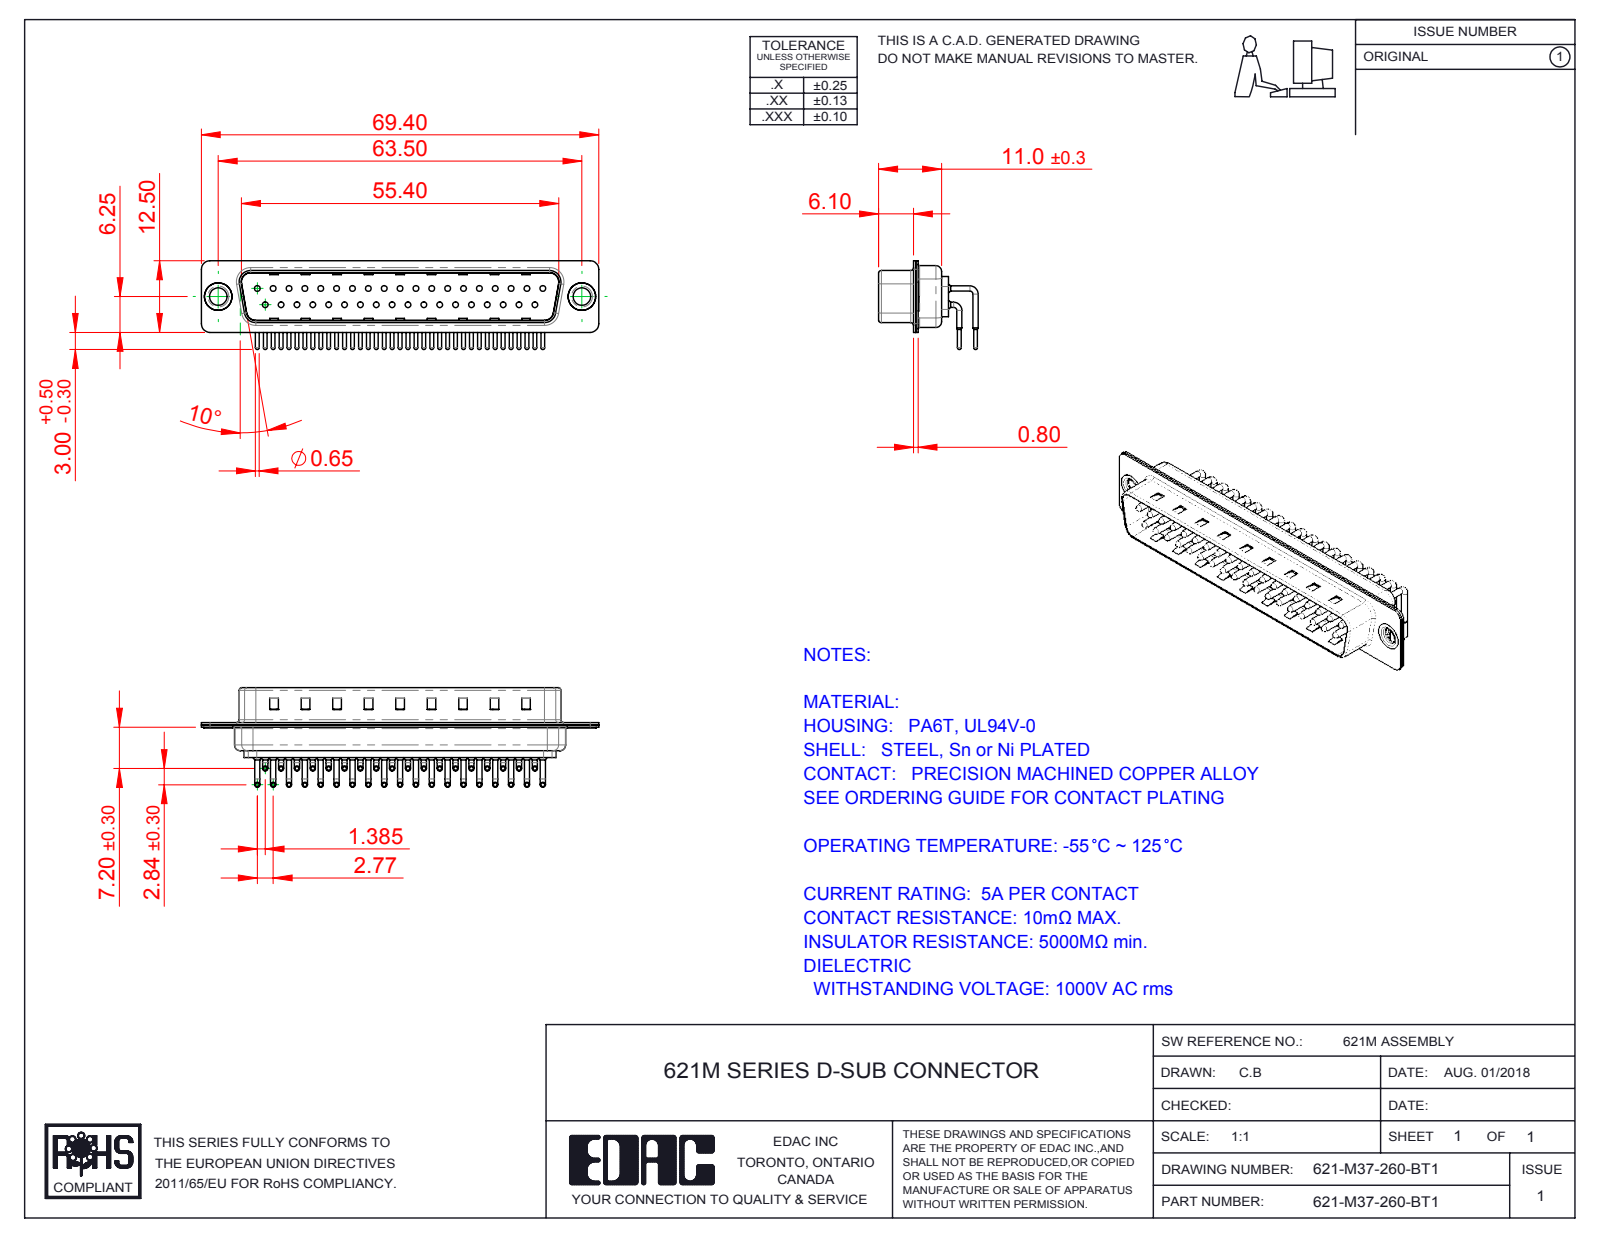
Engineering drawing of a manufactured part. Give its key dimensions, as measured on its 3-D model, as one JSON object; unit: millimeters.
{"part_name": "621-M37-260-BT1; 621M Housing_37 Contacts; 621M Shell Rear_37 Contacts; 621M Contact Row 2 (+3 more)", "step_written_by": "SolidWorks 2016 (CONFIG_CONTROL_DESIGN)", "units": "millimeters", "bodies": {"solids": 42, "faces": 4456, "planar": 2571, "cylindrical": 1457, "other": 428}, "overall_size": [69.4, 17.39, 15.49], "volume_mm3": 3918, "surface_area_mm2": 10217, "round_holes": [[1, 37], [1.7, 37], [2, 37], [3.05, 2], [4, 2], [4.8, 2]], "round_bosses_or_shafts": [[0.9, 74], [1.5, 37], [0.65, 37], [5, 2], [4.9, 2], [3.55, 2]], "partial_cylinders_radius": [[1.01, 37], [1.5, 16], [2, 12], [0.5, 8], [1.6, 8], [0.25, 4], [0.6, 4], [0.65, 4]], "face_to_face_distances": [0.4, 0.85, 9.55, 8.7, 1.25, 10.4, 1.5, 1.9, 0.35, 9.95], "hole_center_spacings": [3.16, 2.77, 5.54, 8.31, 5.04, 10.1, 11.08, 12.78]}
